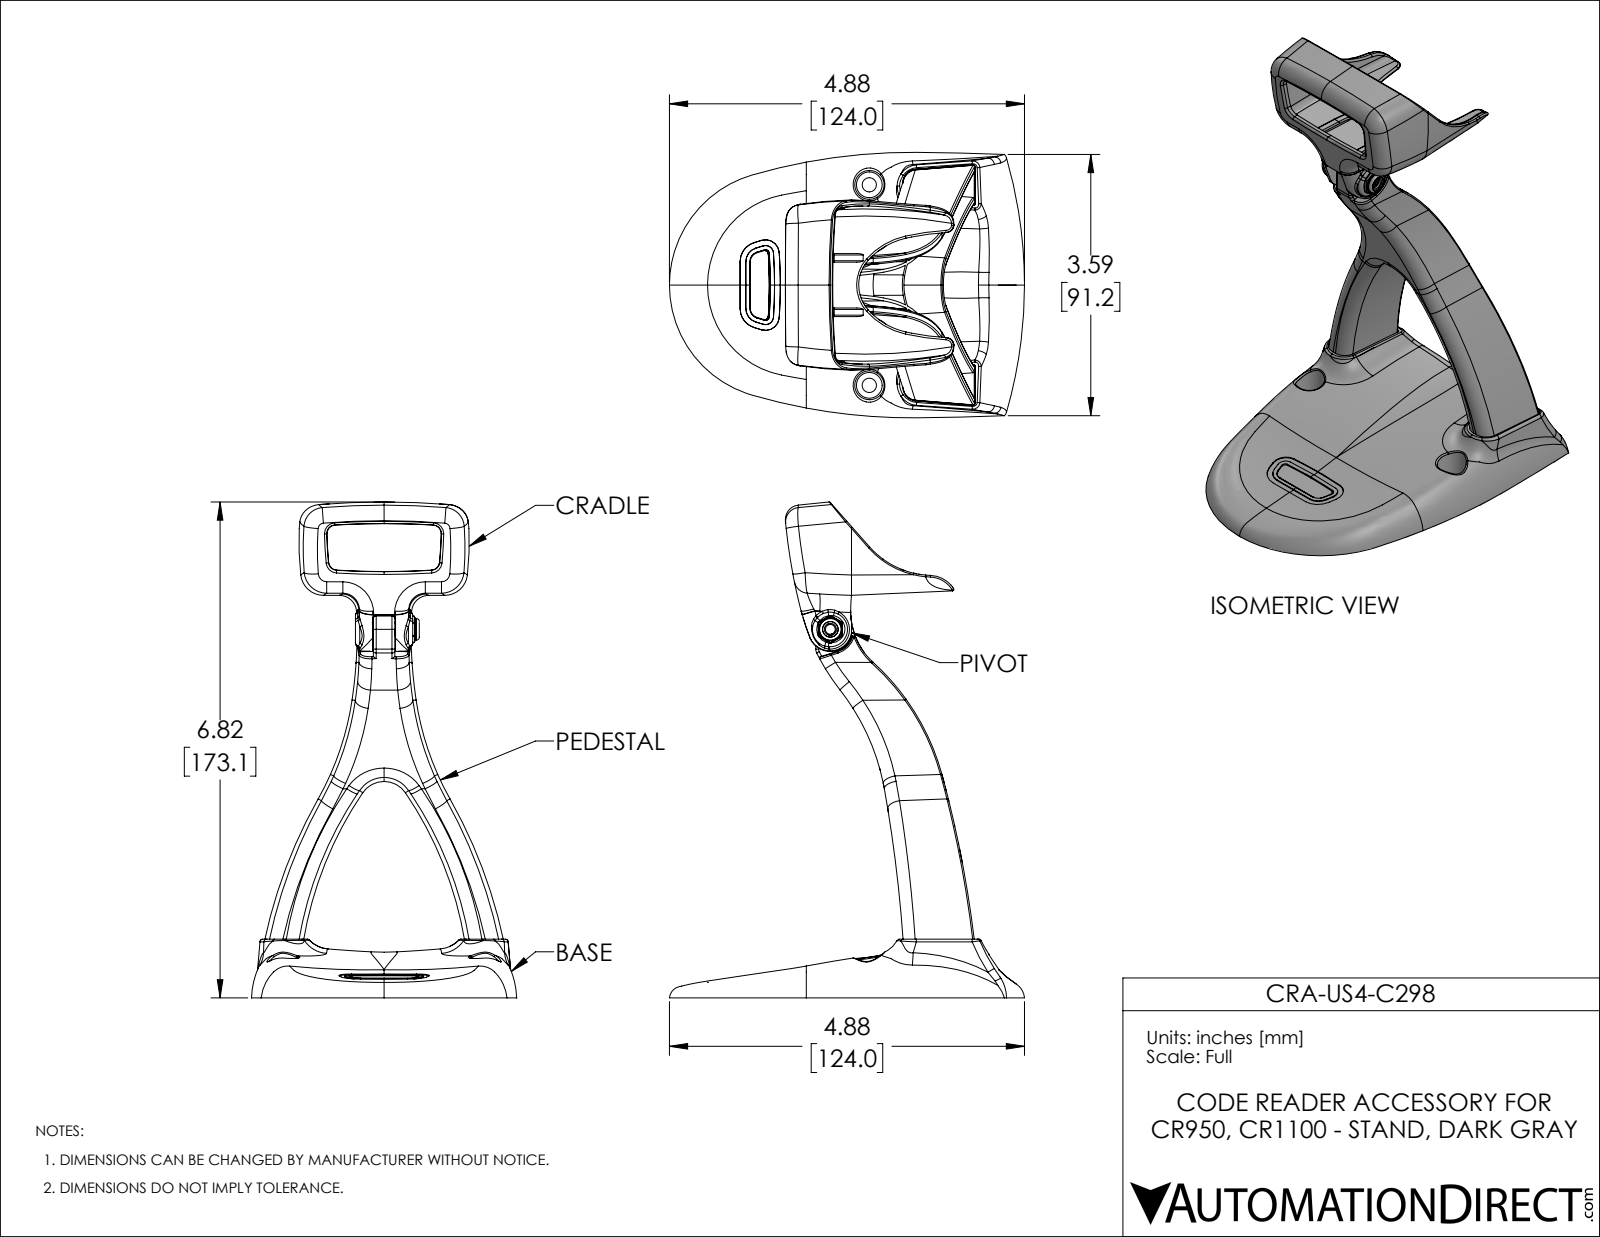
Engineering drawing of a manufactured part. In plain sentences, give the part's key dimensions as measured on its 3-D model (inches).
The part is named "CRA-US9-C298". Its 3-D file was written by "SolidWorks 2019 (AUTOMOTIVE_DESIGN)". It is 3 solids with 1230 faces: 406 planar, 200 cylindrical and 624 other. Overall it measures 6.815 by 4.882 by 3.649 inches. Its volume is 4.792 cubic inches and its surface area 117.6 square inches. Round holes: 3 of diameter 0.197, 2 of diameter 0.138, 1 of diameter 0.165, 1 of diameter 0.209, 1 of diameter 0.213. Round bosses or shafts: 1 of diameter 0.335, 1 of diameter 0.295, 1 of diameter 0.196. Partial cylindrical surfaces (rounded edges, fillets, slot ends): 31 of radius 0.02, 12 of radius 0.039, 8 of radius 0.016, 8 of radius 0.118, 7 of radius 0.079, 5 of radius 0.03, 4 of radius 0.047, 4 of radius 0.984. The main face-to-face distances are 1.437, 1.929, 0.96, 0.96, 0.969, 0.969, 0.039, 2.874, 0.098, 0.622. The hole center spacings are 0.606, 2.756, 2.822.
